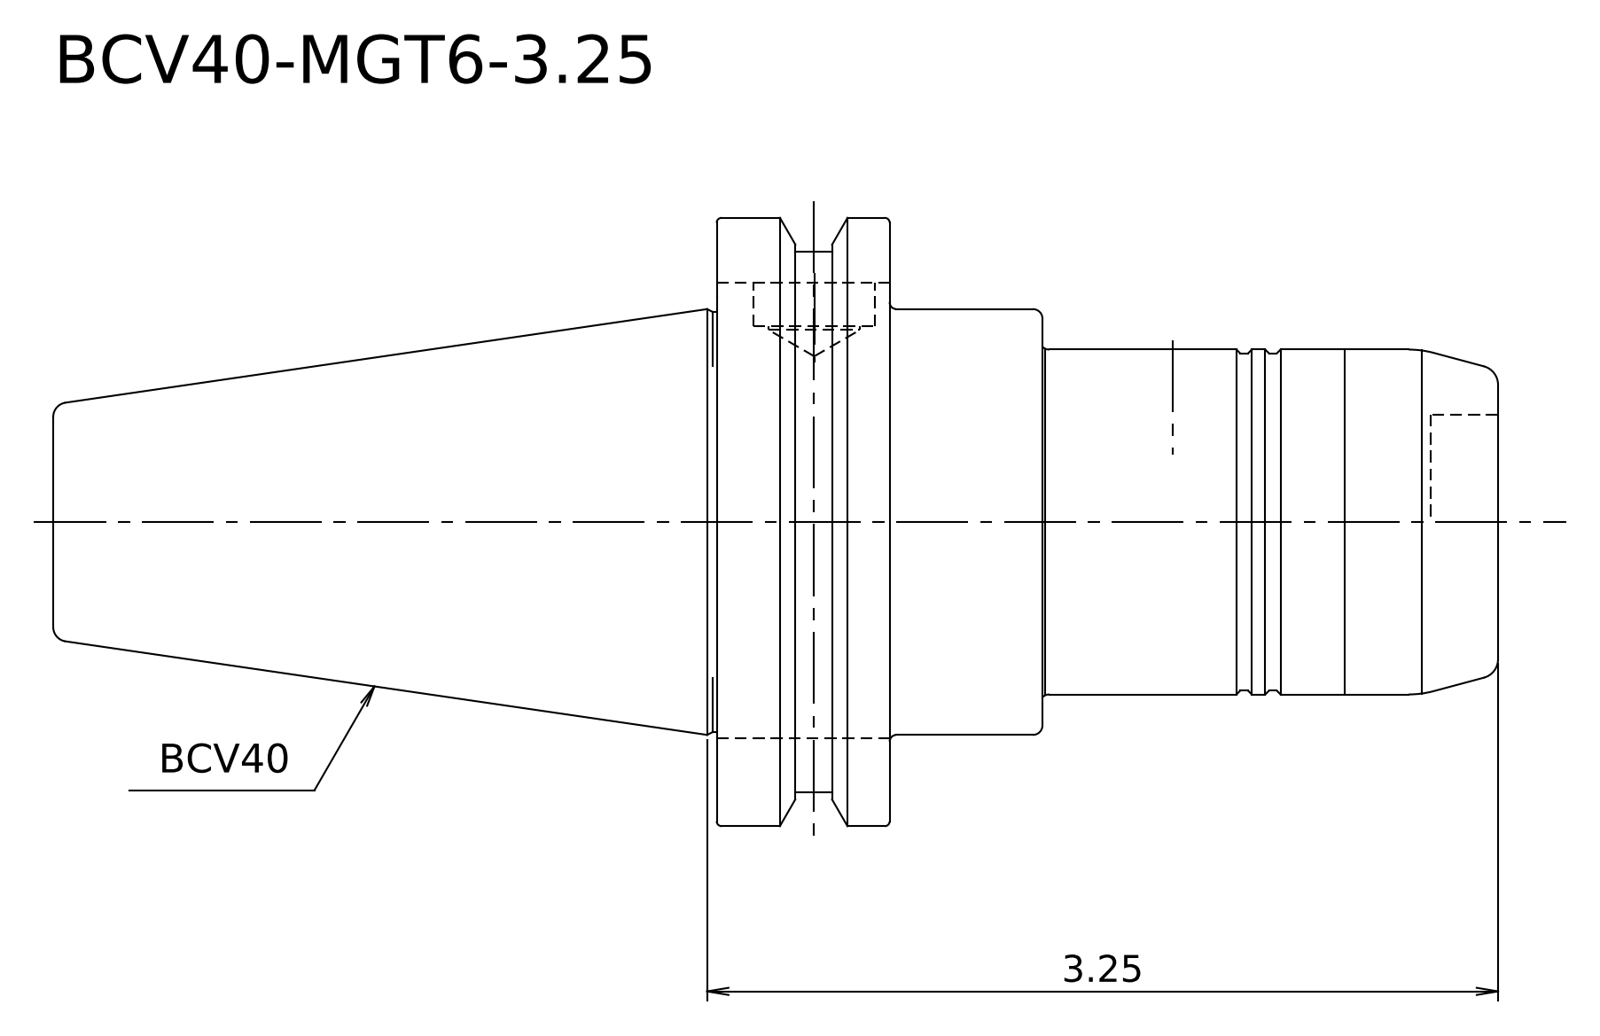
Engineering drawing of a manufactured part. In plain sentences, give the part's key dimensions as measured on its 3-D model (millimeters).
The part is named "BCV40-MGT6-3.25". Its 3-D file was written by "SolidWorks 2014 (AUTOMOTIVE_DESIGN)". It is 1 solid with 156 faces: 39 planar, 43 cylindrical and 74 other. Overall it measures 150.8 by 63.5 by 61.04 millimeters. Its volume is 181 550 cubic millimeters and its surface area 26 170 square millimeters. Round holes: 1 of diameter 9.5, 1 of diameter 12.7, 1 of diameter 13.38, 1 of diameter 16.3. Round bosses or shafts: 1 of diameter 63.5, 1 of diameter 56.36, 1 of diameter 44.45, 1 of diameter 43.85, 1 of diameter 36, 1 of diameter 35.2. Partial cylindrical surfaces (rounded edges, fillets, slot ends): 12 of radius 0.76. The main face-to-face distances are 18.05, 81.55, 63.5, 34.05, 16, 47.5, 17.75, 33.75, 81.25, 69.25.
